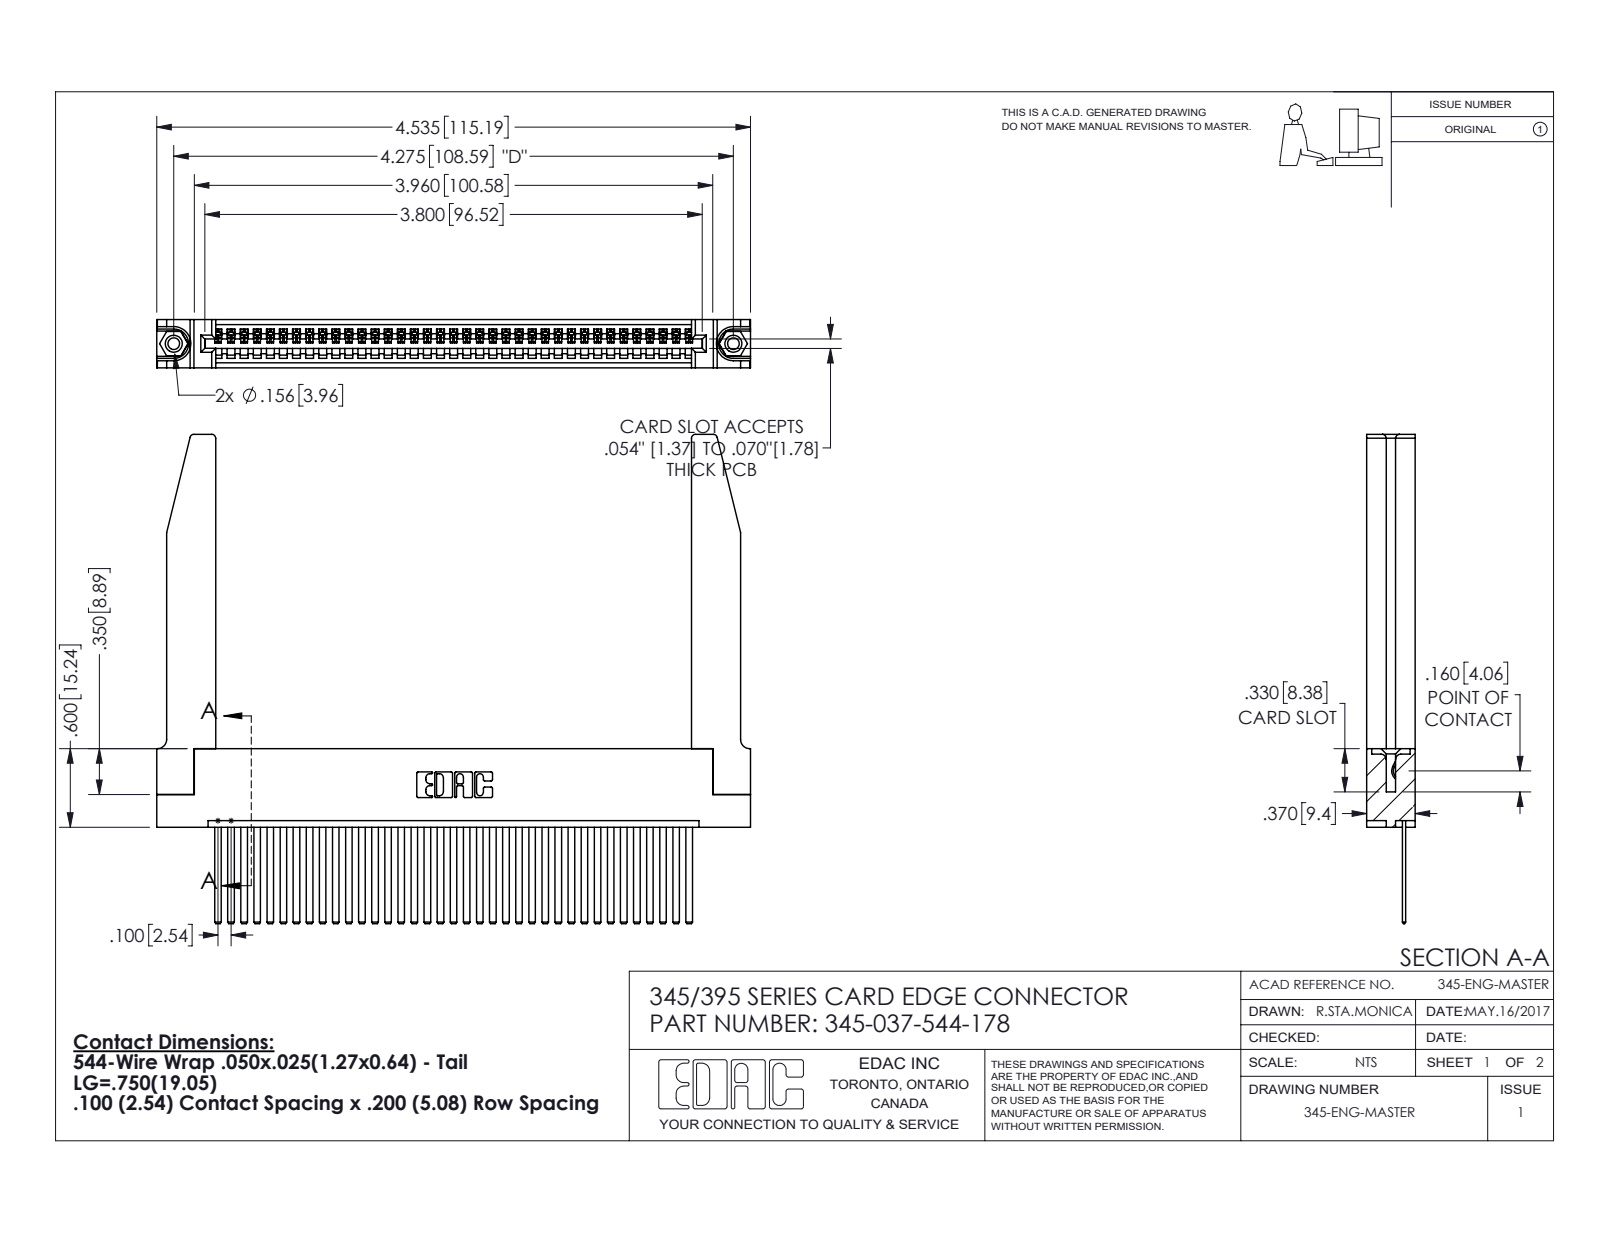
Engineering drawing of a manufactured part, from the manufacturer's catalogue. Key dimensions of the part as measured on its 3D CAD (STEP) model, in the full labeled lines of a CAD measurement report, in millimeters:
Part name (STEP PRODUCT): 345-220-078_345-220-078; 345 Part_Flush Mounting Lugs - 0.156 Dia-TH; 345-037-544-178; 345-250-001_345-250-001-102 (+1 more)
STEP written by: SolidWorks 2016 (CONFIG_CONTROL_DESIGN)
Units: millimetres
Bodies: 42 solids, 2284 faces (1554 planar, 678 cylindrical, 52 other)
Overall size (bounding box): 115.2 × 94.9 × 9.4
Volume: 19 110 mm³ · Surface area: 23 120 mm²
Round holes (diameter × count): ⌀2.3 ×2, ⌀3.2 ×2, ⌀4 ×2, ⌀1.6 ×1
Round bosses / shafts (diameter × count): ⌀3.9 ×2
Partial cylindrical surfaces — rounded edges, fillets, slot ends (radius × count): R0.2 ×74, R0.3 ×22, R0.8 ×8, R0.2 ×6, R0.8 ×6, R0.7 ×3, R0.8 ×2, R1 ×2
Main face-to-face distances: 1.8, 7.6, 9.4, 2.5, 6.9, 0.6, 5.1, 5.7, 3.8, 3.8
Hole centre spacings: 6.9, 102.6, 108.6
